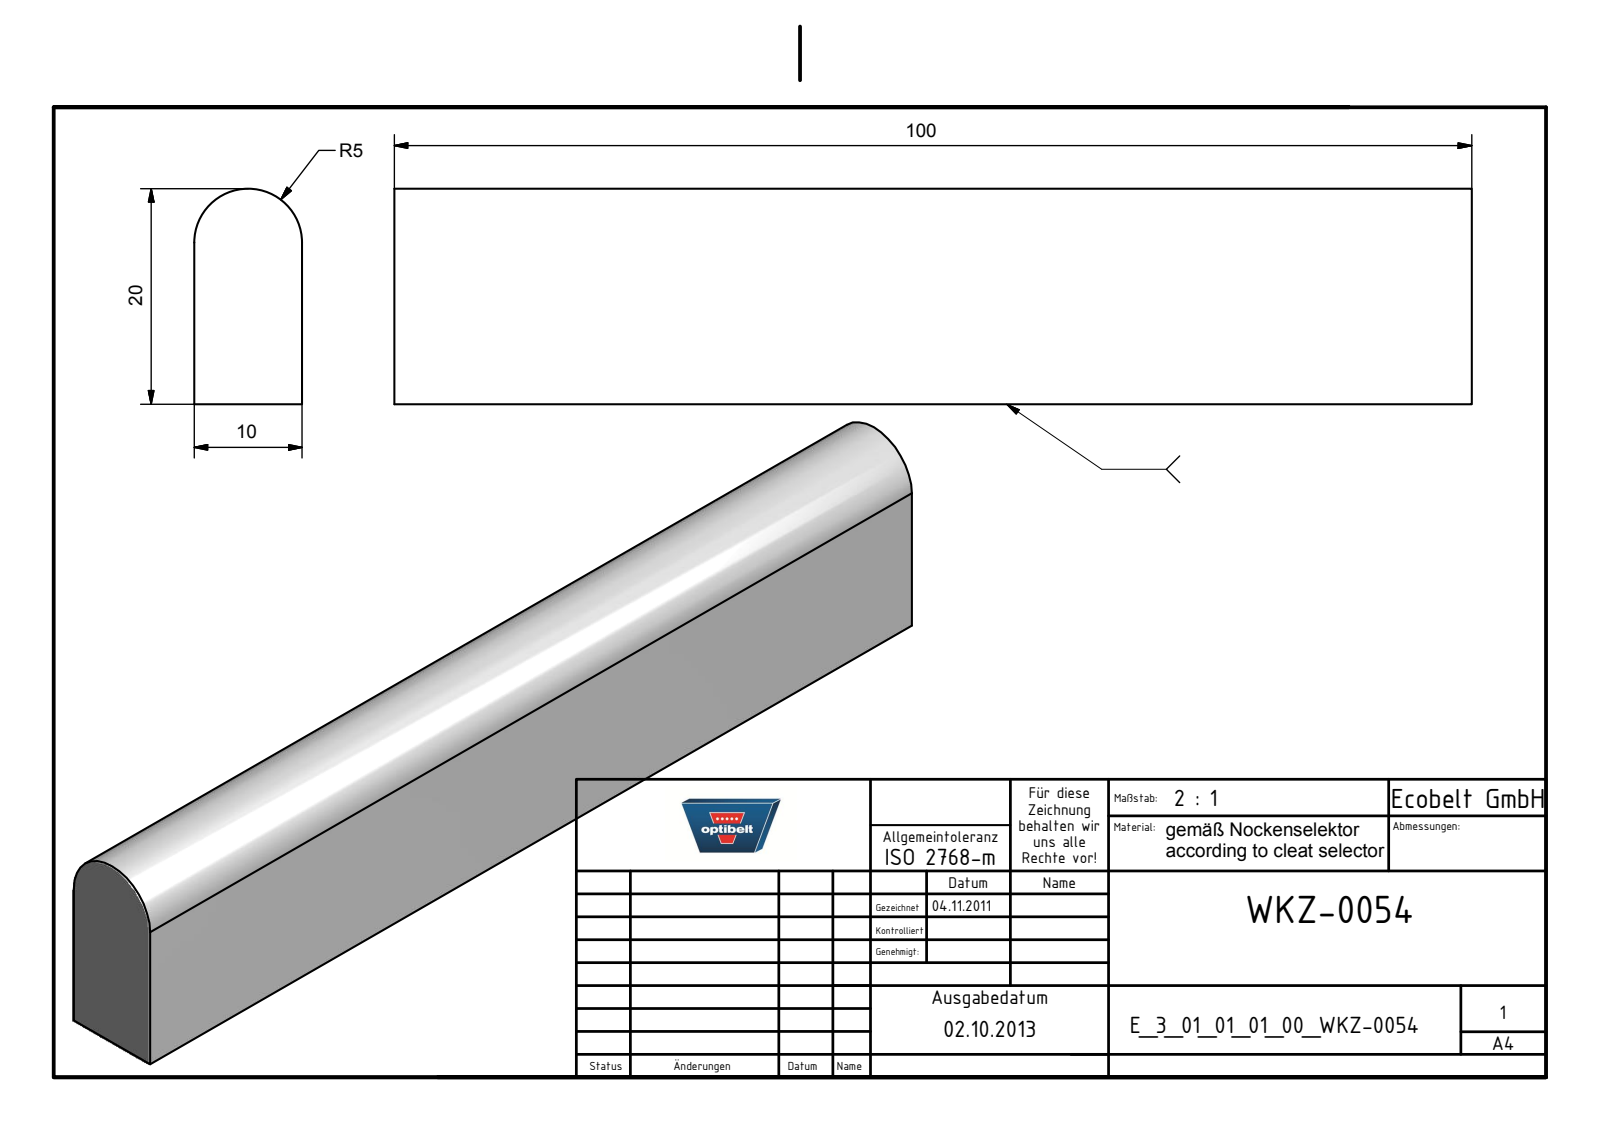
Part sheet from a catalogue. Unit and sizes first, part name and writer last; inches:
Units: inches
Overall size (bounding box): 3.937 × 0.787 × 0.394
Partial cylindrical surfaces — rounded edges, fillets, slot ends (radius × count): R0.197 ×1
Main face-to-face distances: 0.394, 3.937
Volume: 1.155 in³ · Surface area: 9.221 in²
Bodies: 1 solid, 6 faces (5 planar, 1 cylindrical, 0 other)
Part name (STEP PRODUCT): E_3_01_01_01_00_WKZ-0054
STEP written by: Autodesk Inventor 2021 (AUTOMOTIVE_DESIGN)
